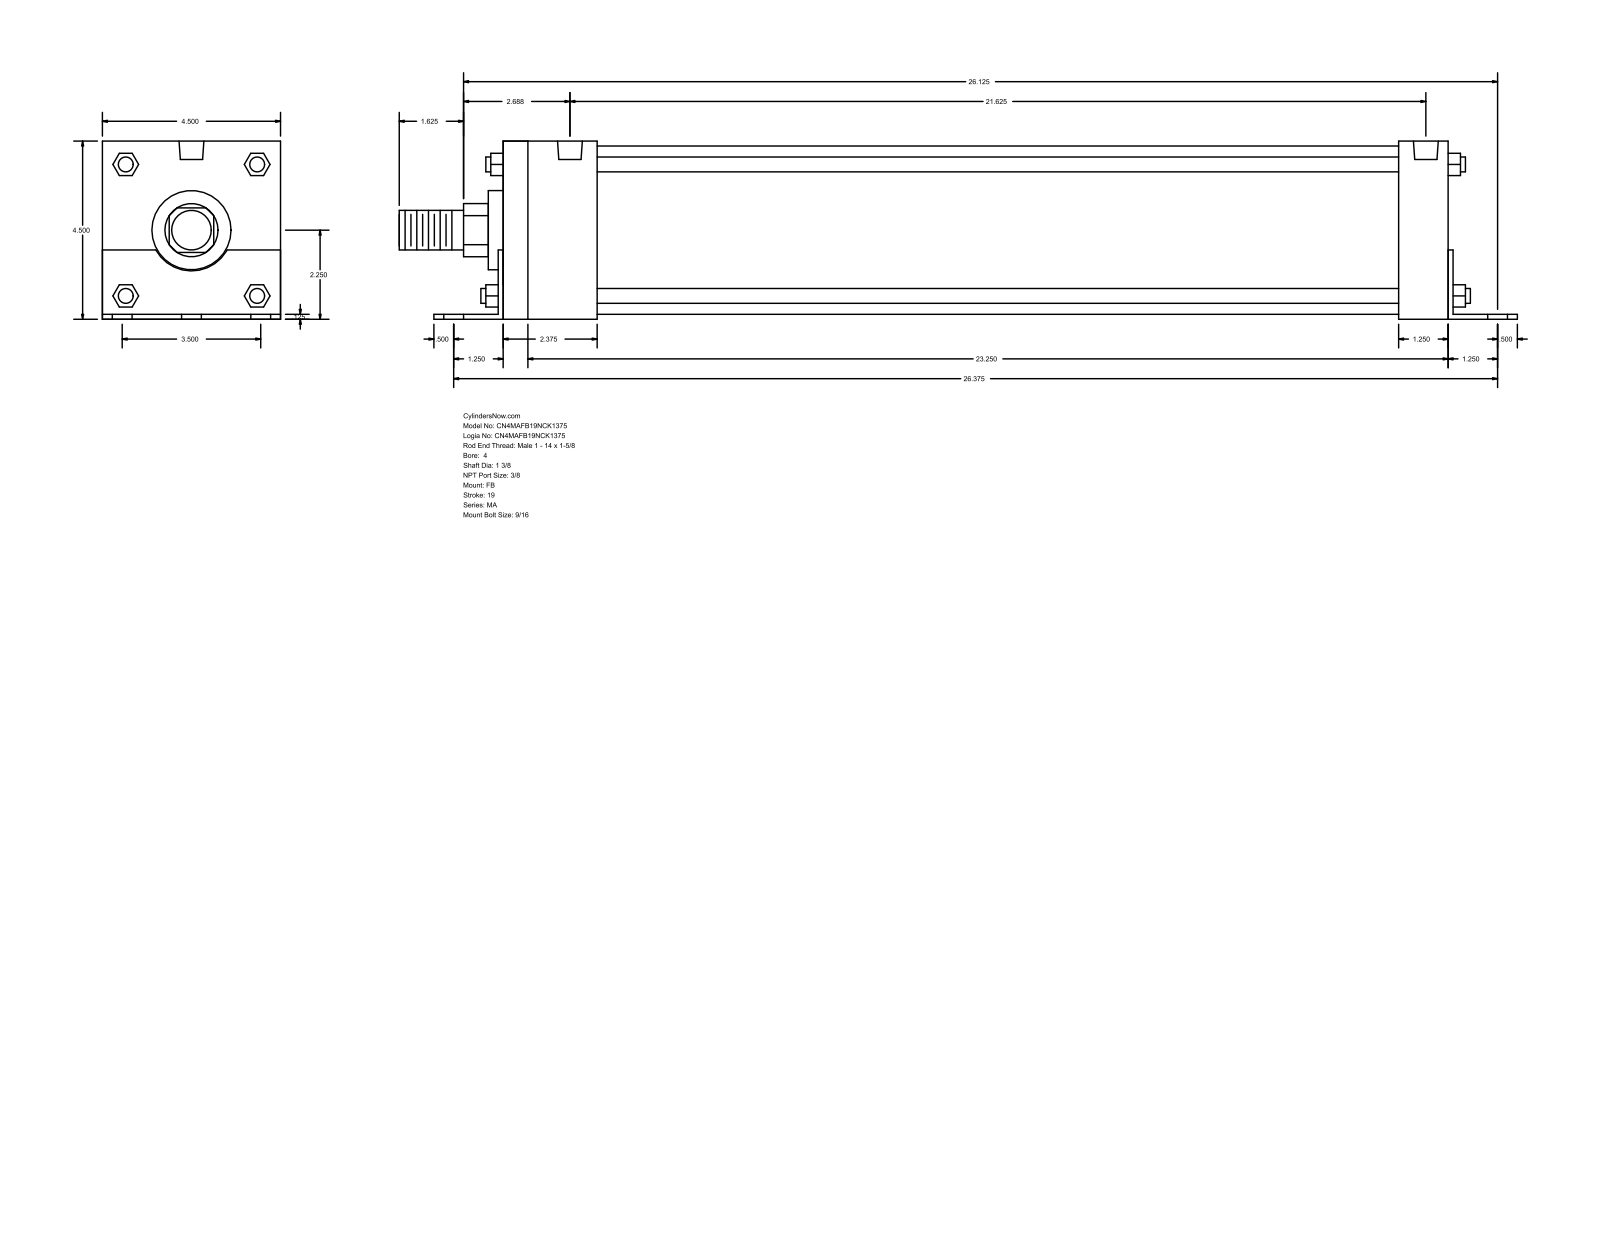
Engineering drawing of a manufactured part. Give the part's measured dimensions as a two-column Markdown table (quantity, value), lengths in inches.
| quantity | value |
| --- | --- |
| part name | MA_FB__0400_1.375 |
| STEP written by | GSSL Pune (CONFIG_CONTROL_DESIGN) |
| units | inches |
| bodies | 0 solids, 140 faces (105 planar, 35 cylindrical, 0 other) |
| overall size | 28.25 × 4.502 × 4.5 |
| round holes (diameter × count) | 0.563 × 6, 0.437 × 4, 0.627 × 2 |
| round bosses / shafts (diameter × count) | 0.375 × 4, 4.25 × 1, 2 × 1, 1.375 × 1, 1 × 1 |
| partial cylindrical surfaces (radius × count) | 0.672 × 1, 1.03 × 1 |
| main face-to-face distances | 4.5, 0.125, 4.502, 0.123, 4.377, 24, 23.875, 24.125, 1.25, 22.75 |
| hole center spacings | 1.75, 26.433, 26.375, 0.188, 2.52, 2.658, 3.419, 3.5 |
